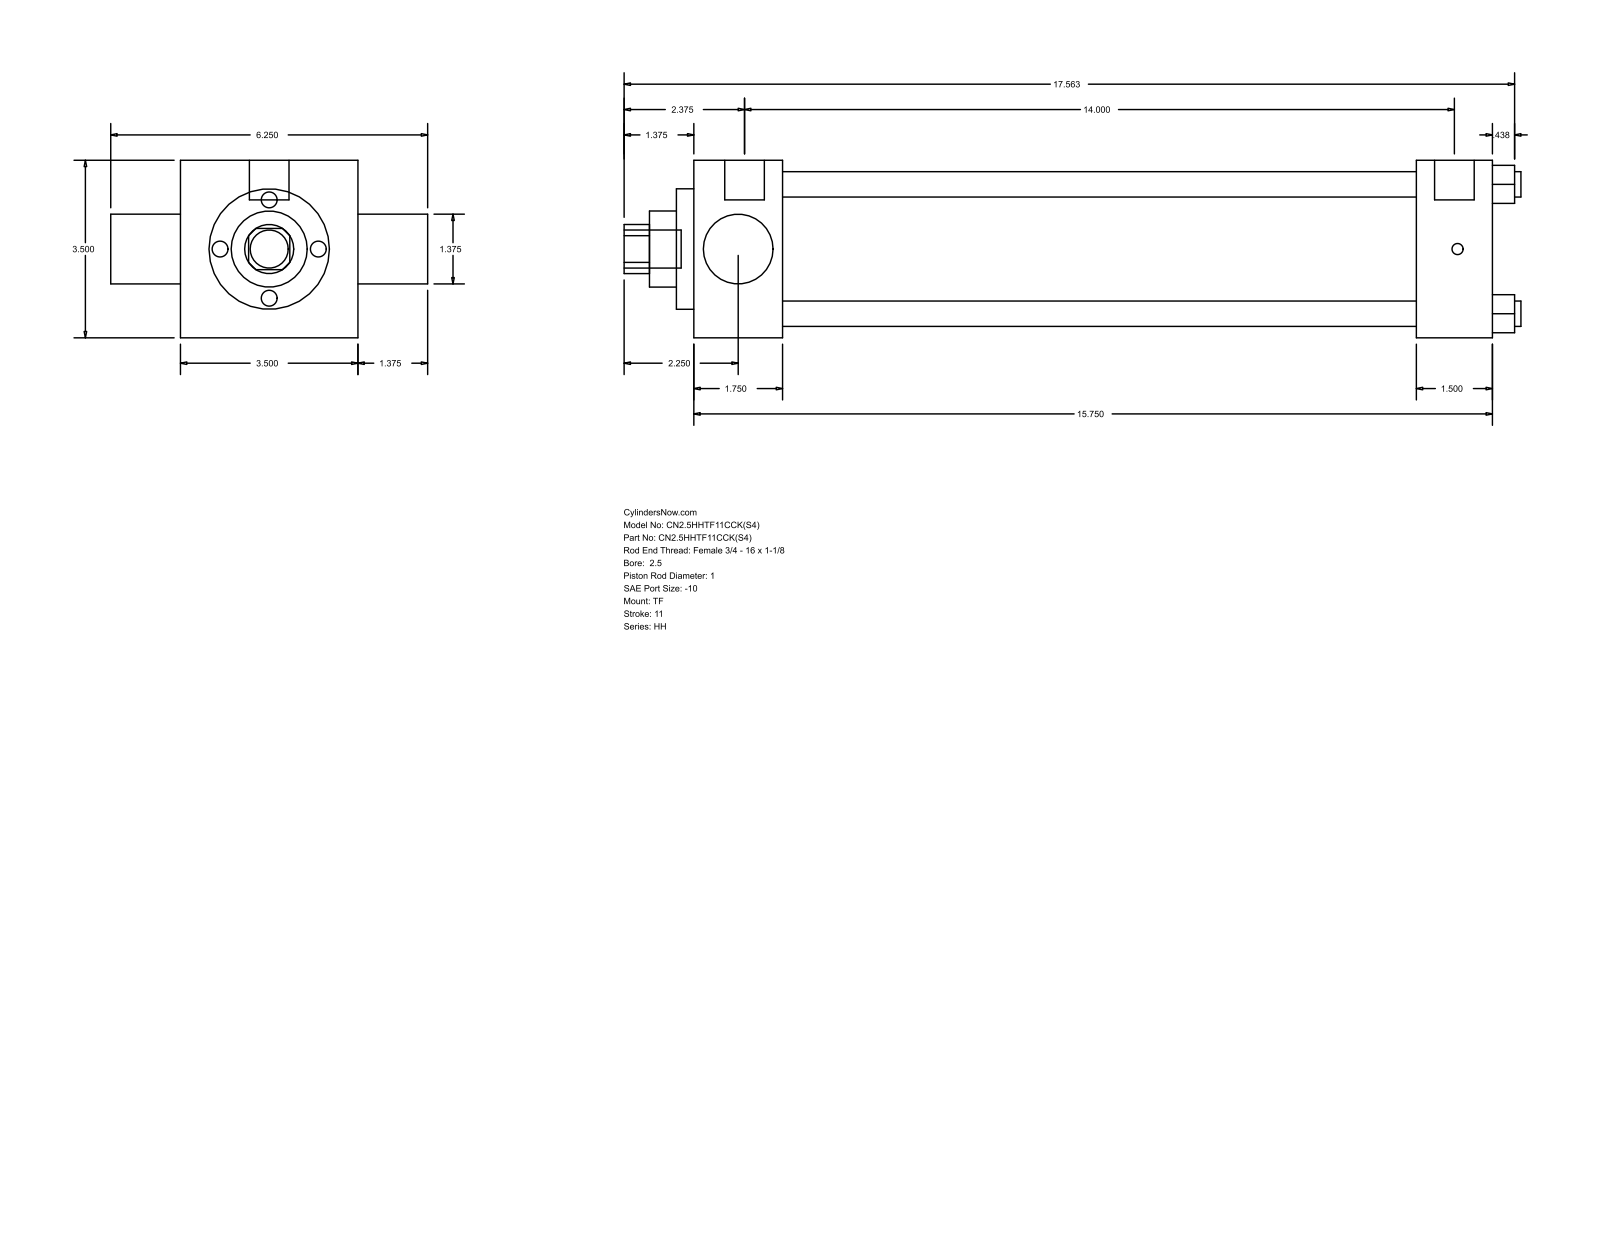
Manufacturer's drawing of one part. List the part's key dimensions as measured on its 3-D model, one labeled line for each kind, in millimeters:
Part name (STEP PRODUCT): HH_TF__0250_1
STEP written by: GSSL Pune (CONFIG_CONTROL_DESIGN)
Units: millimetres
Bodies: 0 solids, 86 faces (61 planar, 25 cylindrical, 0 other)
Overall size (bounding box): 449.26 × 158.75 × 88.9
Round holes (diameter × count): ⌀12.7 ×4, ⌀25.4 ×1, ⌀34.92 ×1, ⌀38.1 ×1, ⌀60.33 ×1, ⌀73.03 ×1
Round bosses / shafts (diameter × count): ⌀5.56 ×3, ⌀19.84 ×2, ⌀19.05 ×1
Partial cylindrical surfaces — rounded edges, fillets, slot ends (radius × count): R12.29 ×1
Main face-to-face distances: 88.9, 400.06, 44.46, 355.6, 361.96, 317.5, 38.1, 34.93, 123.83, 8.73
Hole centre spacings: 45.79, 64.76, 91.58
